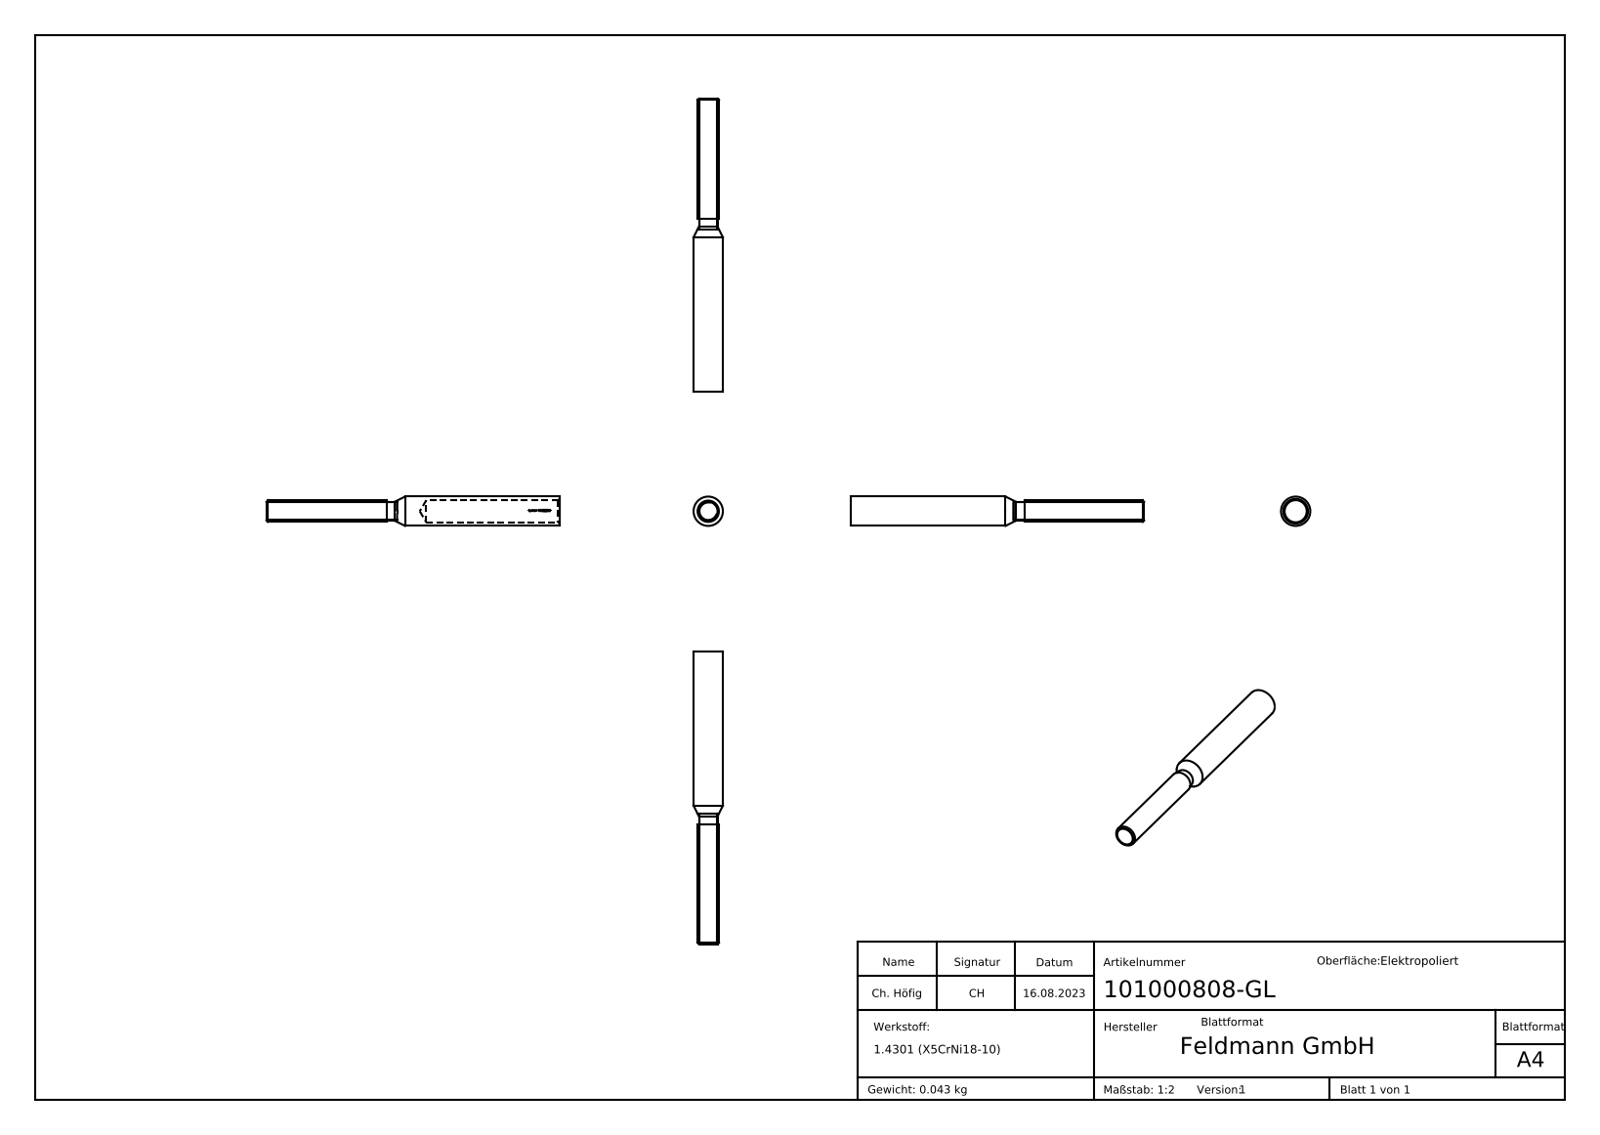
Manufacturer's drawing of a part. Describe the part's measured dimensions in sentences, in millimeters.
The part is named "101000808-GL". Its 3-D file was written by "SolidWorks 2018 (CONFIG_CONTROL_DESIGN)". It is 1 solid with 259 faces: 83 planar, 36 cylindrical and 140 other. Overall it measures 110 by 11 by 11 millimeters. Its volume is 5 391 cubic millimeters and its surface area 4 787 square millimeters. Round holes: 1 of diameter 8.3. Round bosses or shafts: 1 of diameter 11, 1 of diameter 8, 1 of diameter 7. Partial cylindrical surfaces (rounded edges, fillets, slot ends): 1 of radius 4.25. The main face-to-face distances are 110, 65, 45, 7.5, 3.07, 0.82, 3.89, 4.43, 3.61, 0.81.
